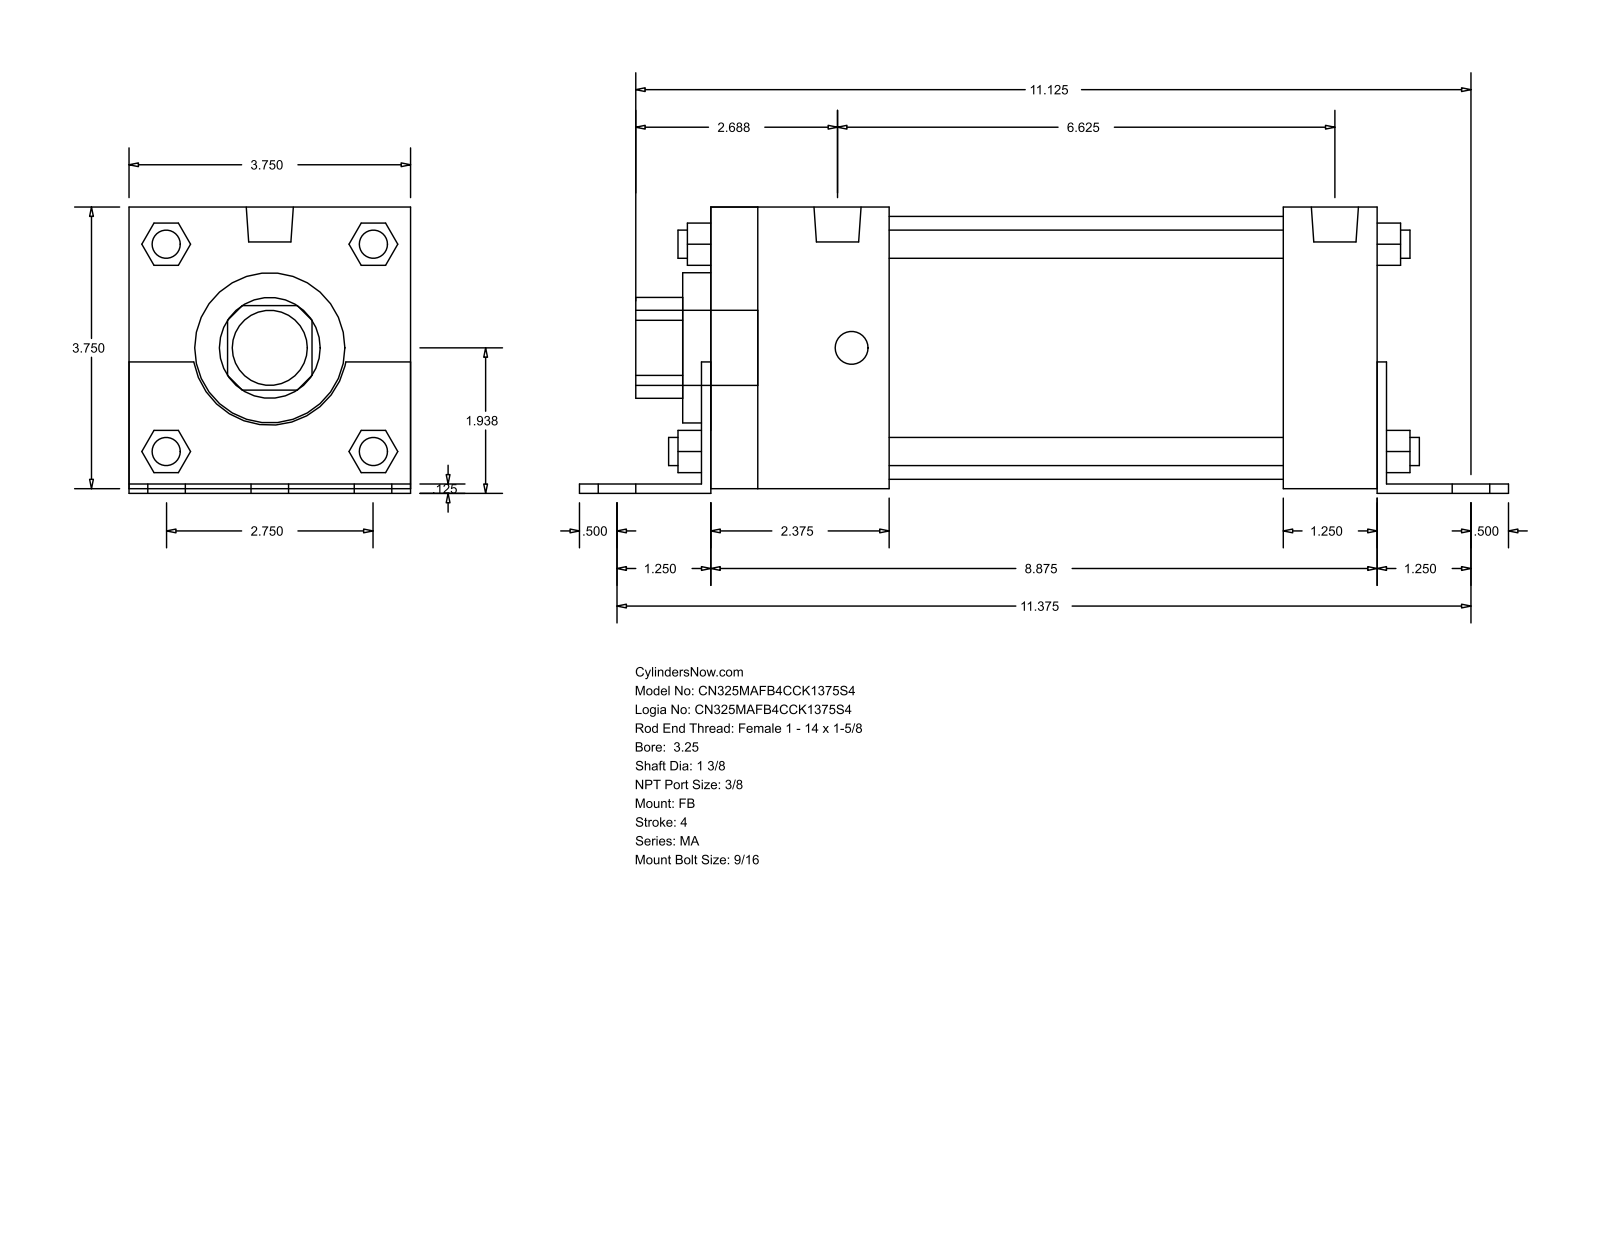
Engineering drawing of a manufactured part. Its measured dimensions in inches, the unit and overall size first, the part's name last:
Units: inches
Overall size (bounding box): 12.375 × 3.813 × 3.75
Round holes (diameter × count): ⌀1.375 ×1, ⌀2 ×1, ⌀3.5 ×1
Round bosses / shafts (diameter × count): ⌀0.563 ×6, ⌀0.437 ×4, ⌀0.375 ×4, ⌀0.627 ×2, ⌀1 ×1
Partial cylindrical surfaces — rounded edges, fillets, slot ends (radius × count): R0.672 ×1, R1.03 ×1
Main face-to-face distances: 3.75, 0.125, 0.063, 3.812, 0.062, 3.687, 0.125, 8.875, 9, 1.25
Bodies: 0 solids, 140 faces (105 planar, 35 cylindrical, 0 other)
Part name (STEP PRODUCT): MA_FB__0325_1.375
STEP written by: GSSL Pune (CONFIG_CONTROL_DESIGN)
